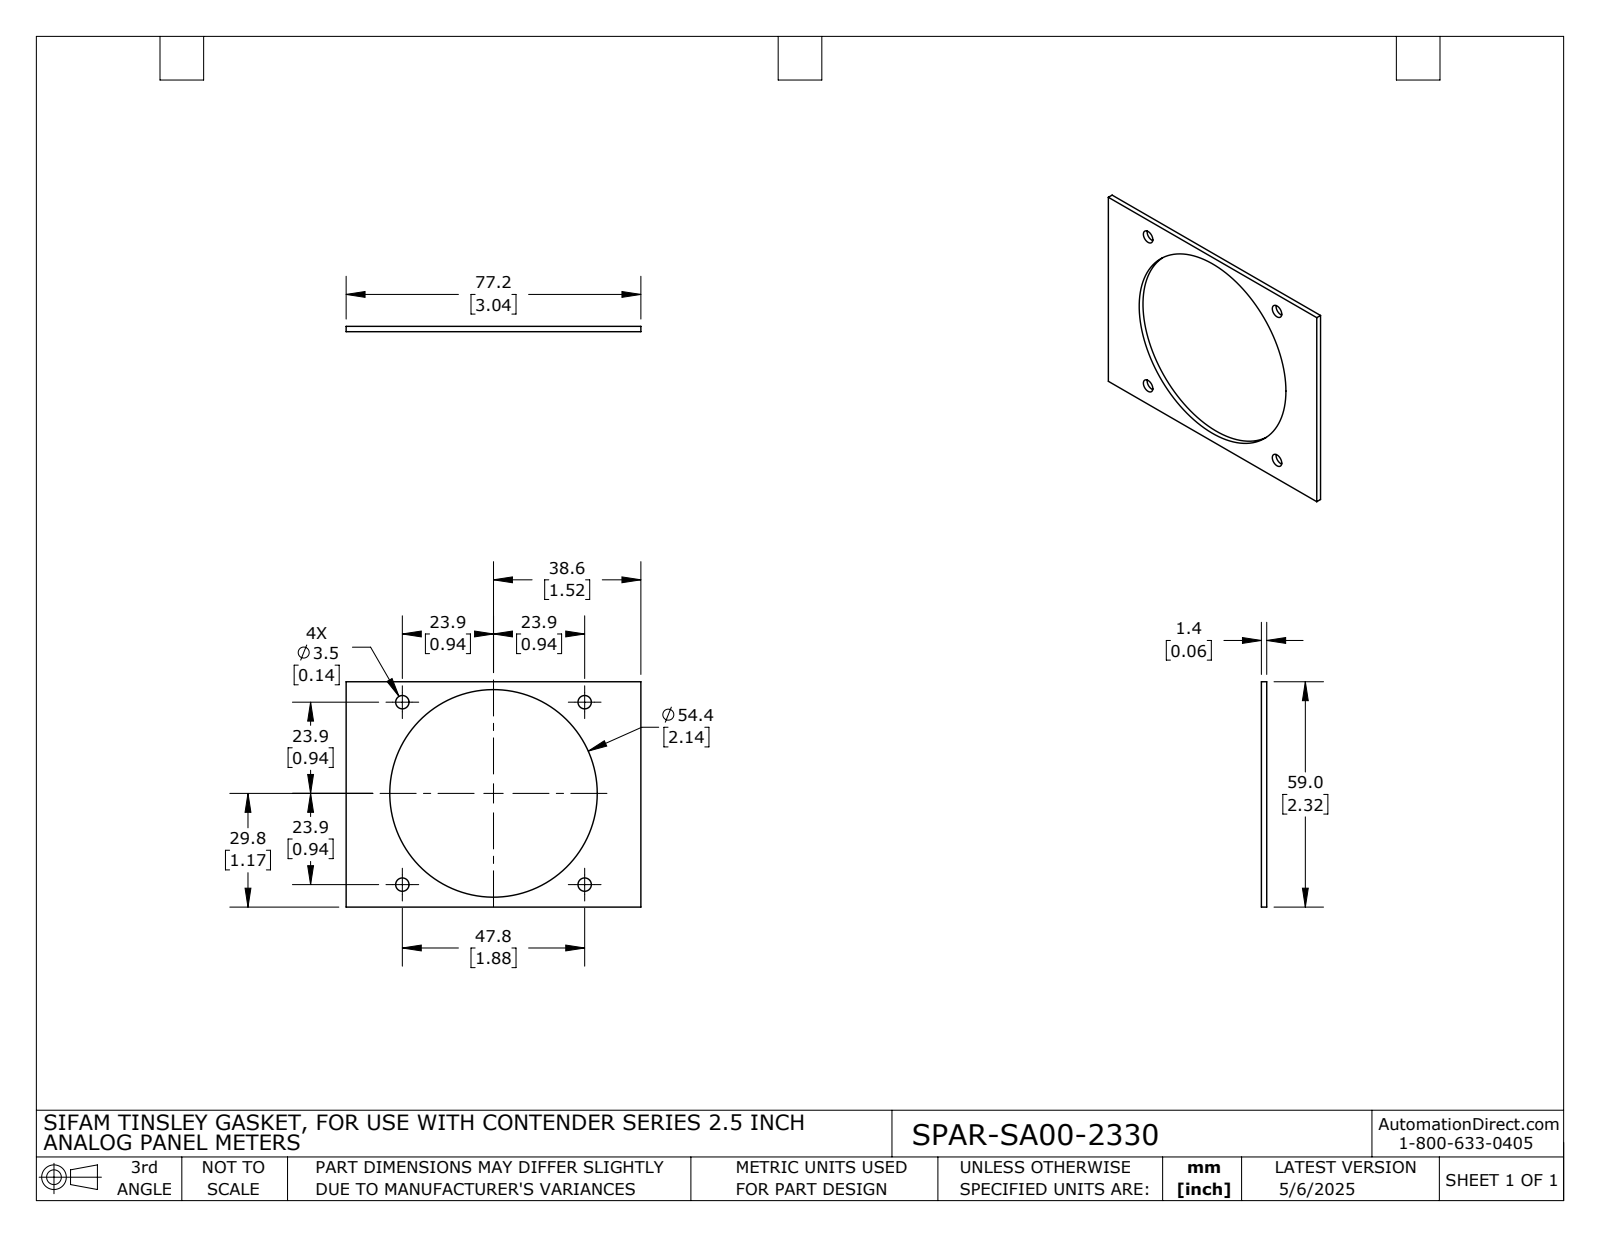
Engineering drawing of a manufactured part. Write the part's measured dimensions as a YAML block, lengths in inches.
part_name: "SPAR-SA00-2330"
step_written_by: "SolidWorks 2021 (AUTOMOTIVE_DESIGN)"
units: inches
bodies: {solids: 1, faces: 16, planar: 6, cylindrical: 10, other: 0}
overall_size: [3.039, 2.323, 0.055]
volume: 0.188
surface_area: 7.866
round_holes:
  - {diameter: 0.138, count: 4}
  - {diameter: 2.14, count: 1}
face_to_face_distances: [0.055, 2.323, 3.039]
hole_center_spacings: [1.33, 1.88, 2.659]
